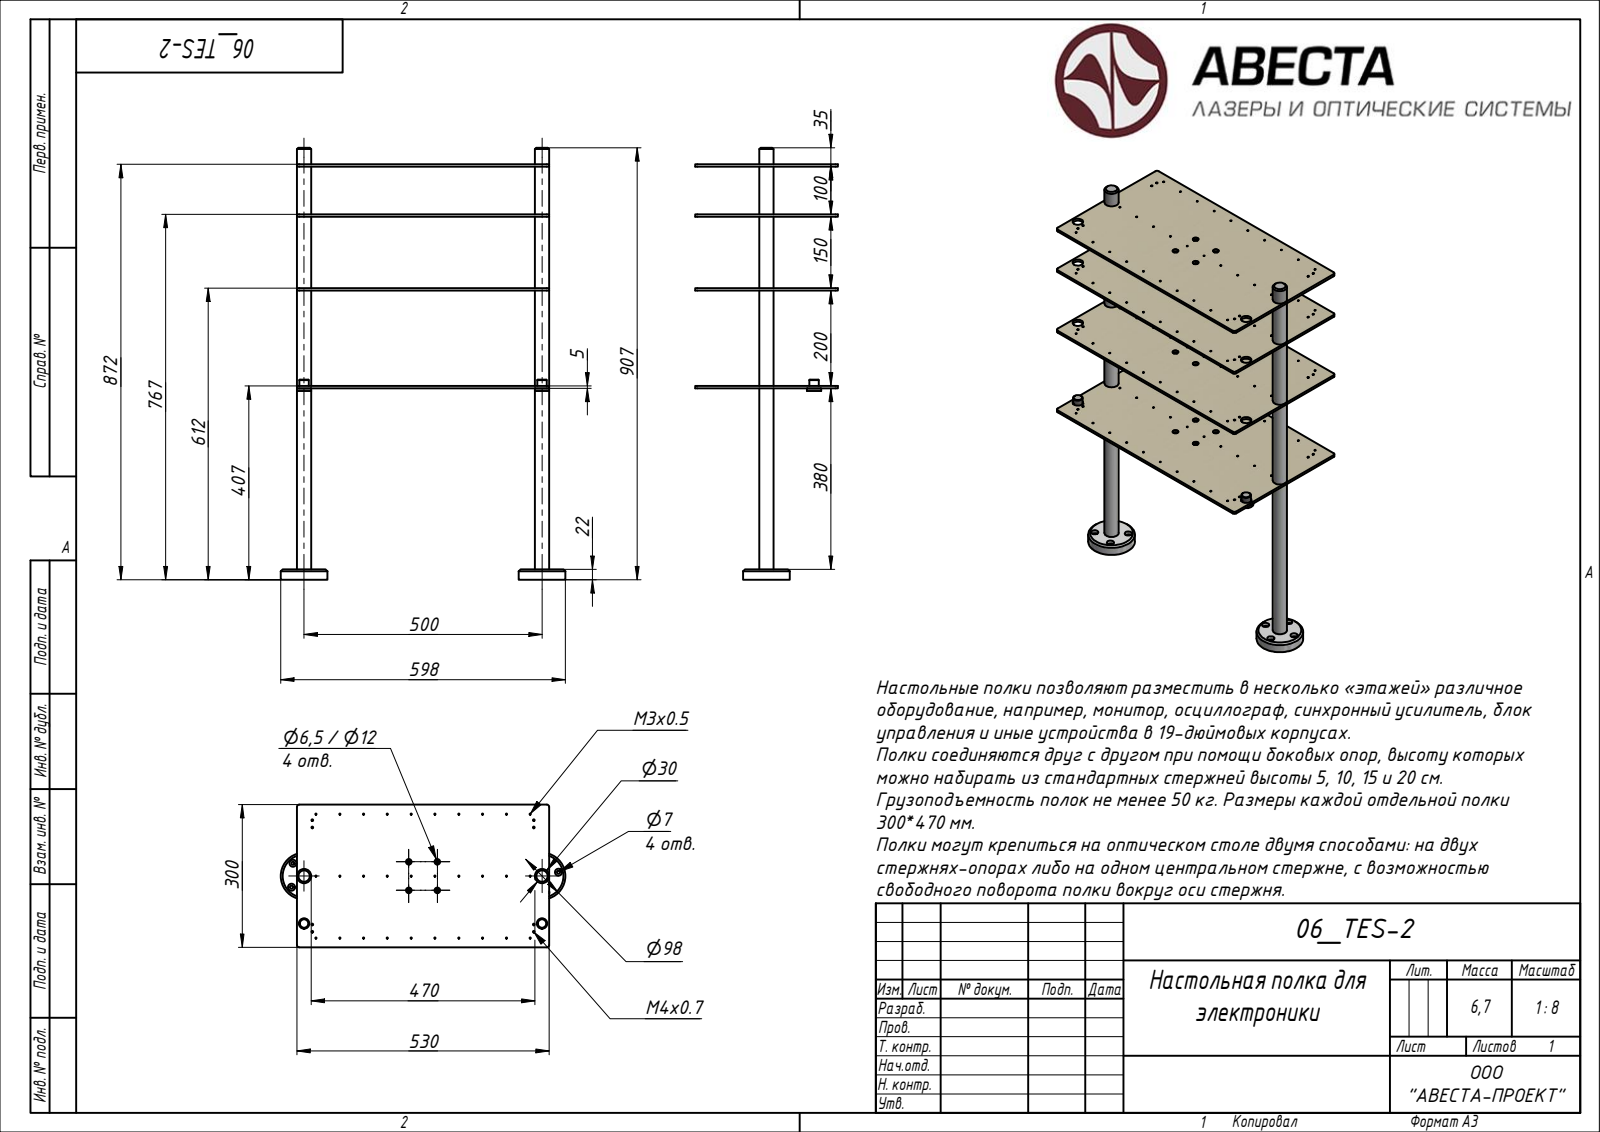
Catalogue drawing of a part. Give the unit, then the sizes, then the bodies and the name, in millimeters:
Units: millimetres
Overall size (bounding box): 907 × 598 × 300
Round holes (diameter × count): ⌀2.5 ×30, ⌀3.2 ×8, ⌀7 ×8, ⌀15 ×8, ⌀6.5 ×4, ⌀12 ×4, ⌀22 ×4, ⌀17.84 ×2, ⌀18.92 ×2, ⌀60 ×2
Round bosses / shafts (diameter × count): ⌀30 ×4, ⌀20 ×4, ⌀18 ×4, ⌀98 ×2
Partial cylindrical surfaces — rounded edges, fillets, slot ends (radius × count): R5 ×4
Main face-to-face distances: 5, 205, 360, 155, 465, 260, 105, 210, 365, 200
Hole centre spacings: 50, 100, 139.28, 164.01, 150, 198.49, 200, 238.54
Volume: 4 686 000 mm³ · Surface area: 1 560 000 mm²
Bodies: 18 solids, 410 faces (82 planar, 280 cylindrical, 48 other)
Part name (STEP PRODUCT): 06_TES-2; T01_Основание; T06_Стержень 400; T05_Стержень 200 (+5 more)
STEP written by: Autodesk Inventor 2020 (AUTOMOTIVE_DESIGN)
